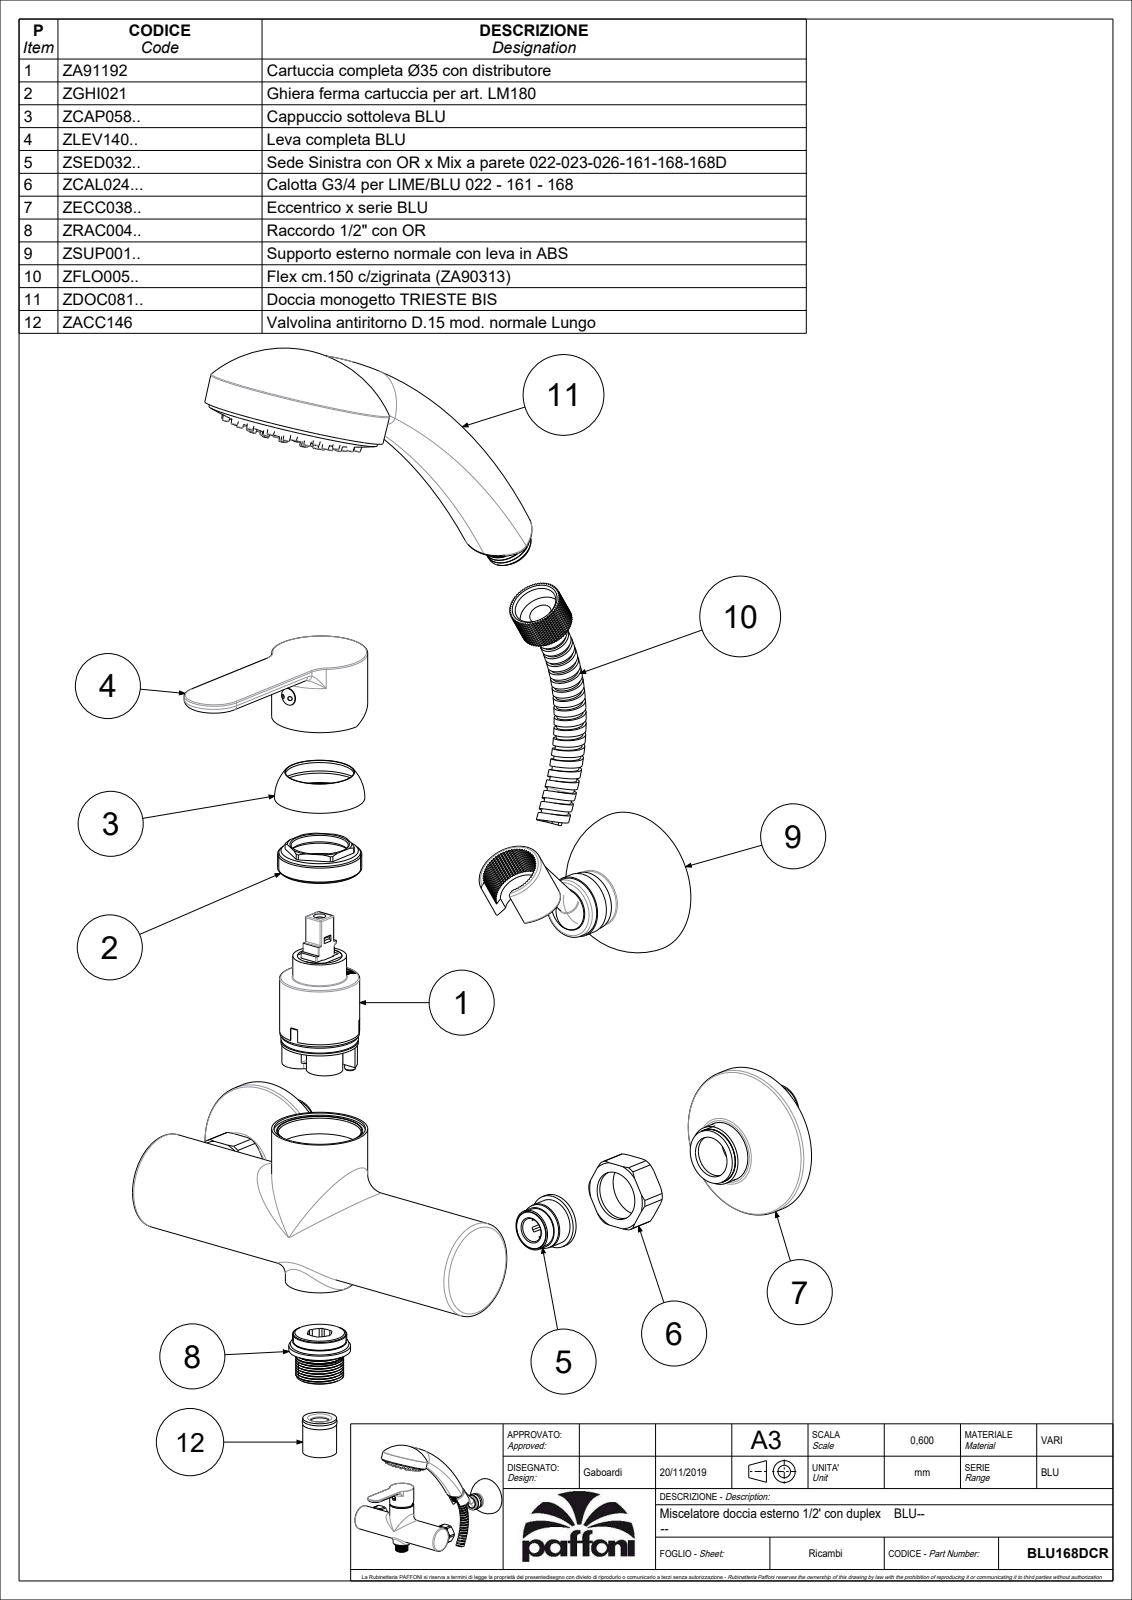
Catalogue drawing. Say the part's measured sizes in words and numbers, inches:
The part is named "BLU168DCR". Its 3-D file was written by "CREO PARAMETRIC BY PTC INC, 2020044 (CONFIG_CONTROL_DESIGN)". It is 8 solids with 1973 faces: 830 planar, 744 cylindrical and 399 other. Overall it measures 11.673 by 11.179 by 9.291 inches. Its volume is 21.36 cubic inches and its surface area 300.9 square inches. Round holes: 48 of diameter 0.059, 5 of diameter 0.472, 3 of diameter 0.354, 3 of diameter 0.709, 2 of diameter 0.13, 2 of diameter 0.276, 2 of diameter 0.315, 2 of diameter 0.591, 2 of diameter 0.642, 2 of diameter 0.669, 2 of diameter 0.846, 2 of diameter 0.949. Round bosses or shafts: 48 of diameter 0.118, 2 of diameter 2.579, 2 of diameter 1.654, 2 of diameter 1.115, 2 of diameter 1.063, 2 of diameter 0.984, 2 of diameter 0.965, 2 of diameter 0.945. Partial cylindrical surfaces (rounded edges, fillets, slot ends): 64 of radius 0.02, 20 of radius 0.012, 13 of radius 0.039, 9 of radius 0.047, 3 of radius 0.207, 3 of radius 0.285, 3 of radius 0.394, 2 of radius 0.008. The main face-to-face distances are 0.079, 4.291, 2.717, 7.008, 4.37, 2.638, 0.709, 0.039, 0.787, 2.795. The hole center spacings are 1.169, 0.411, 0.633, 0.967, 0.591, 0.919, 1.12, 1.234.
